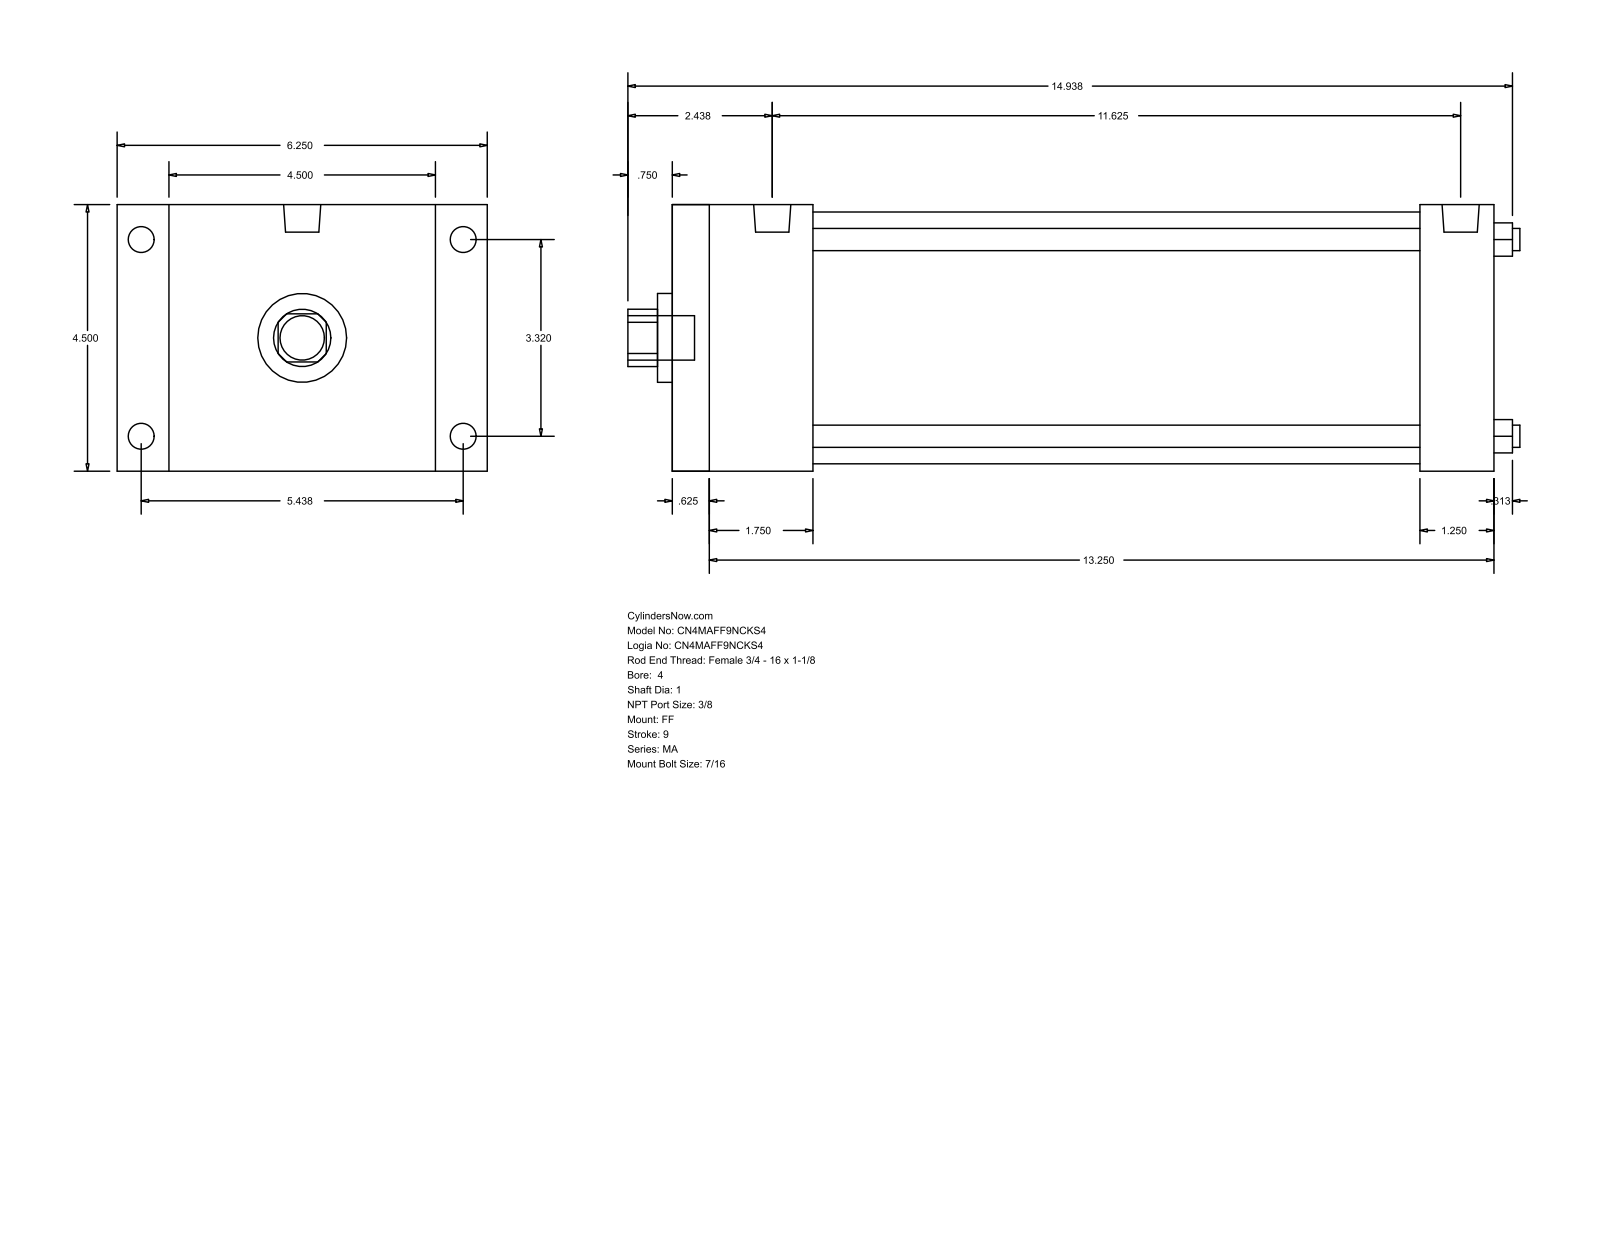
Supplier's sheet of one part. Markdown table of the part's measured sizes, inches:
| quantity | value |
| --- | --- |
| part name | MA_FF__0400_1 |
| STEP written by | GSSL Pune (CONFIG_CONTROL_DESIGN) |
| units | inches |
| bodies | 0 solids, 92 faces (64 planar, 28 cylindrical, 0 other) |
| overall size | 15.063 × 6.25 × 4.5 |
| round holes (diameter × count) | 0.375 × 4, 1 × 1, 1.5 × 1, 4.25 × 1 |
| round bosses / shafts (diameter × count) | 0.437 × 8, 0.627 × 2, 0.75 × 1 |
| partial cylindrical surfaces (radius × count) | 0.484 × 1 |
| main face-to-face distances | 4.5, 13.875, 0.625, 13.25, 0.875, 5.375, 12.625, 12, 1.25, 2.375 |
| hole center spacings | 2.347, 3.32, 4.695 |
